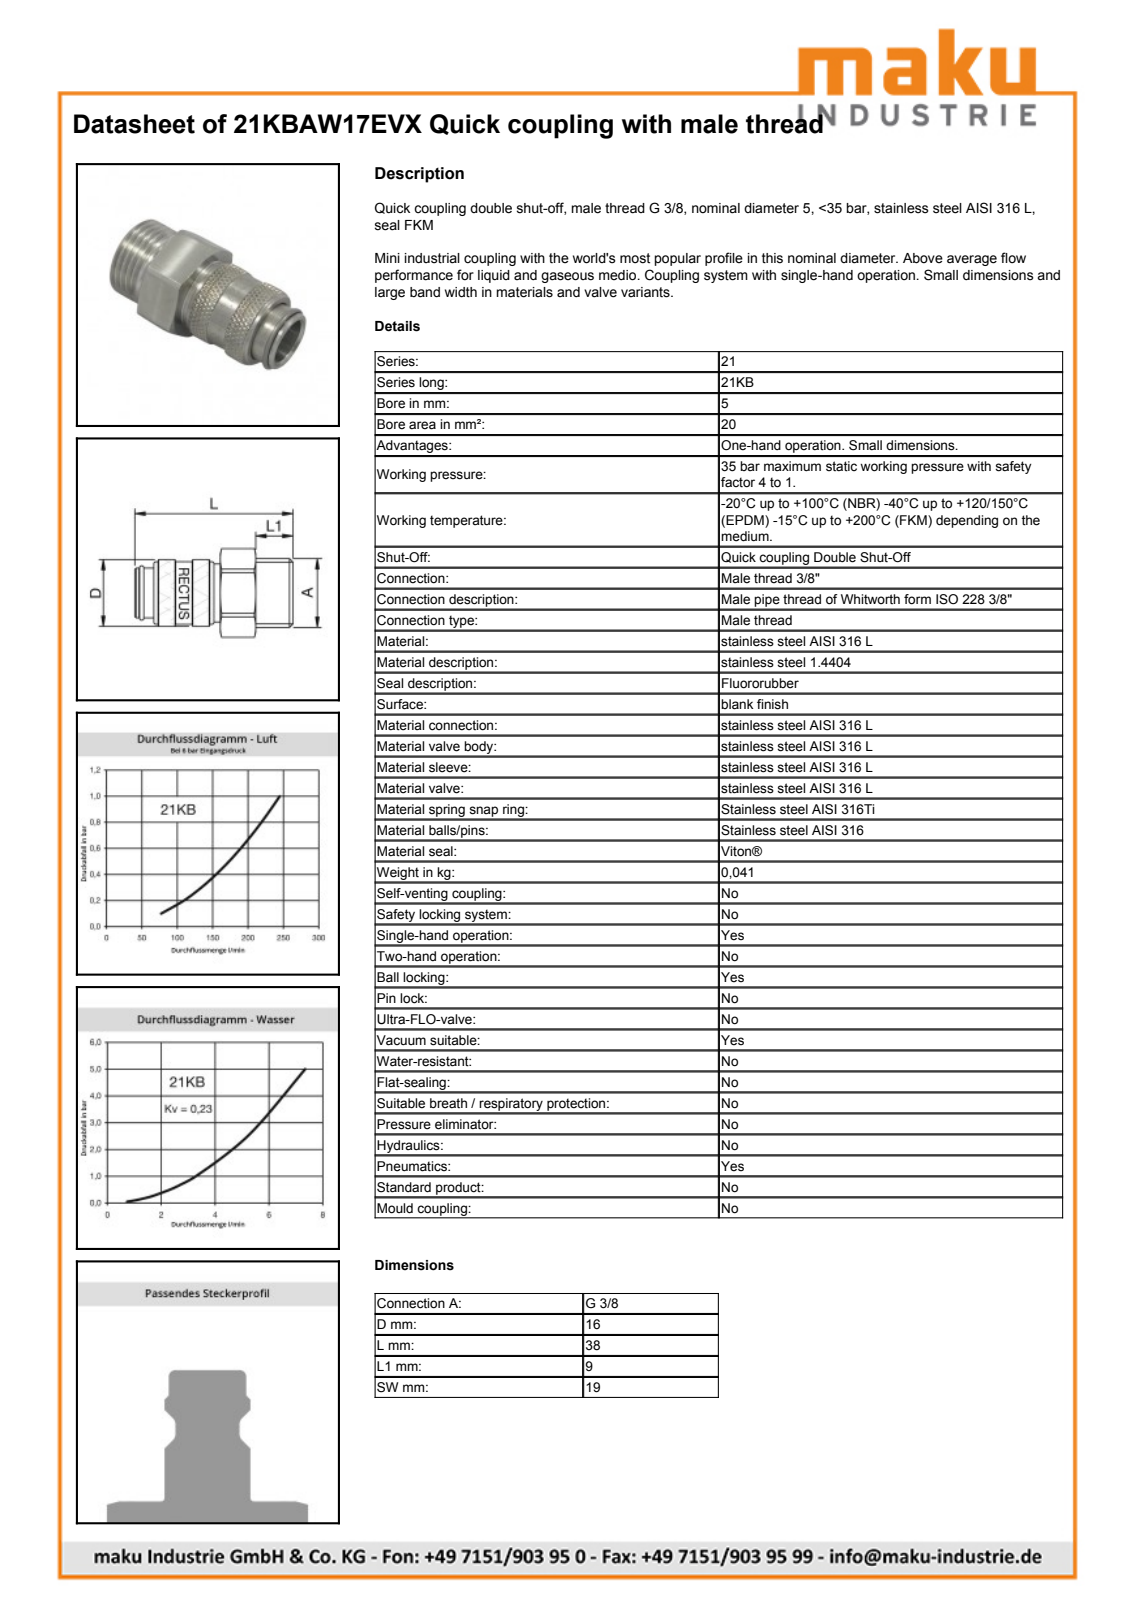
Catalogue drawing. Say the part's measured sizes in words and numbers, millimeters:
The part is named "D105845". Its 3-D file was written by "Autodesk Inventor 2011 (AUTOMOTIVE_DESIGN)". It is 2 solids with 450 faces: 149 planar, 59 cylindrical and 242 other. Overall it measures 38.15 by 21 by 20.79 millimeters. Its volume is 7 853 cubic millimeters and its surface area 3 889 square millimeters. Round holes: 1 of diameter 12.15, 1 of diameter 14. Round bosses or shafts: 1 of diameter 16.66, 1 of diameter 16.15, 1 of diameter 15.1, 1 of diameter 12, 1 of diameter 11.15. Partial cylindrical surfaces (rounded edges, fillets, slot ends): 1 of radius 5.43, 1 of radius 7.45, 1 of radius 10.7. The main face-to-face distances are 19, 17.55, 20.6, 38.15, 29.15, 8.55, 9, 16.15, 4.45, 13.
